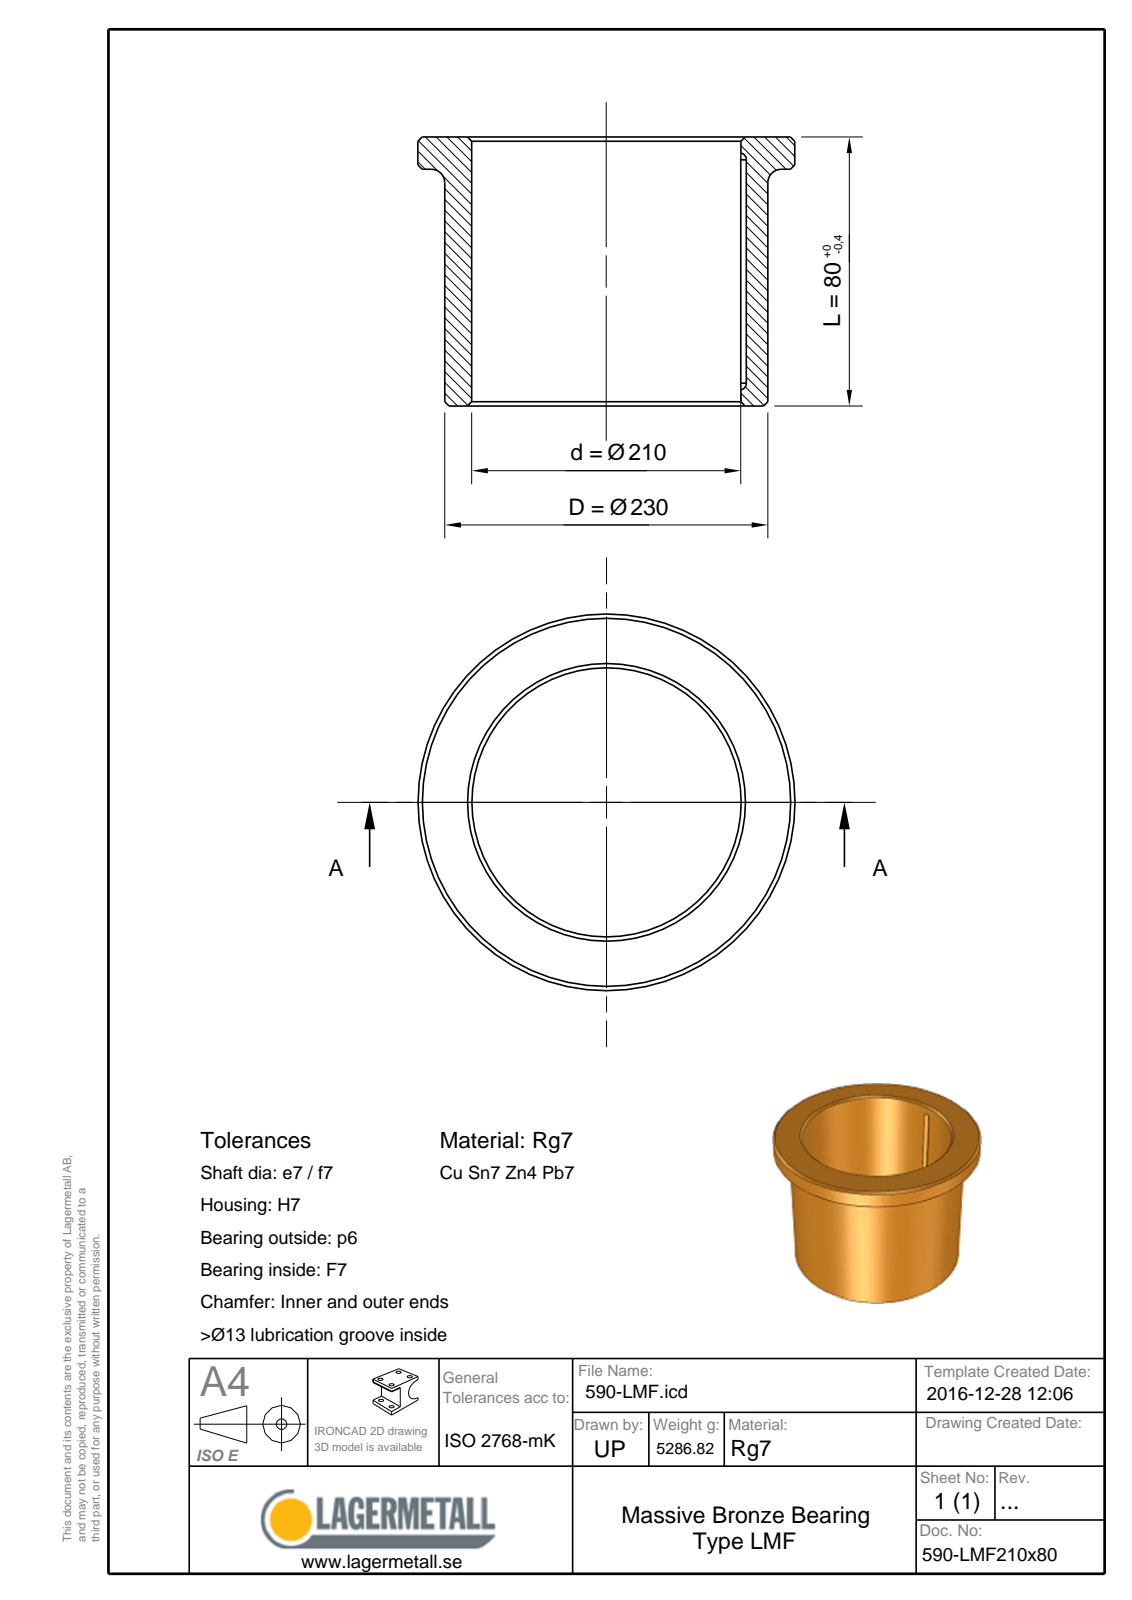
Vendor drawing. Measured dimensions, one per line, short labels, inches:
name: 590-LMF210x80
written by: Spatial InterOp 3D (CONFIG_CONTROL_DESIGN)
unit: in
bodies: 1 solid, 16 faces (6 planar, 5 cylindrical, 5 other)
size: 9.646 × 9.646 × 3.15
volume: 36.66 in³; area: 205 in²
holes: 1× ⌀8.268
bosses: 1× ⌀9.646, 1× ⌀9.055
rounds: 2× R0.108
face distances: 3.15, 2.756, 0.394, 0.217
